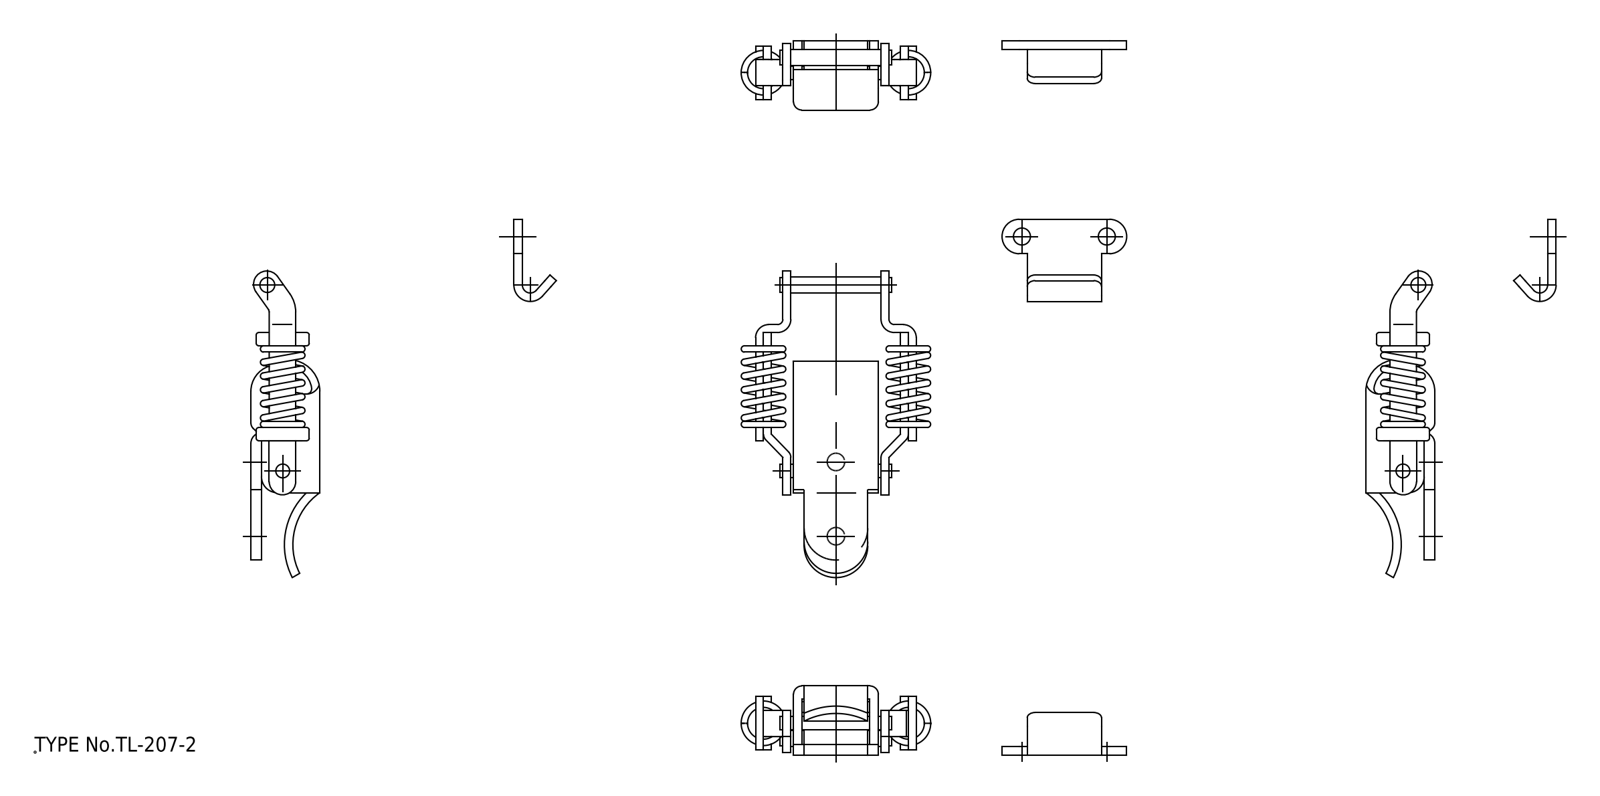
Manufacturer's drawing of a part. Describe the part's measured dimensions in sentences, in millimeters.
The part is named "アーム(A); アーム(B); ベース; レバー (+3 more)". Its 3-D file was written by "spGate 19.8.4 (****-****-****-****) (AUTOMOTIVE_DESIGN)". It is 7 solids with 240 faces: 124 planar, 88 cylindrical and 28 other. Overall it measures 67.55 by 35.73 by 13 millimeters. Its volume is 4 800 cubic millimeters and its surface area 7 822 square millimeters. Round holes: 2 of diameter 3.2, 2 of diameter 3.3. Round bosses or shafts: 1 of diameter 3, 1 of diameter 2.8, 1 of diameter 2.6. Partial cylindrical surfaces (rounded edges, fillets, slot ends): 9 of radius 0.5, 7 of radius 1.5, 7 of radius 2.5, 3 of radius 1, 3 of radius 6, 2 of radius 1.6, 2 of radius 2, 2 of radius 3. The main face-to-face distances are 1.6, 2, 1.5, 11.4, 5.65, 21.65, 27.3, 7.25, 20.05, 14.4. The hole center spacings are 43.25, 57.06, 14, 16.
